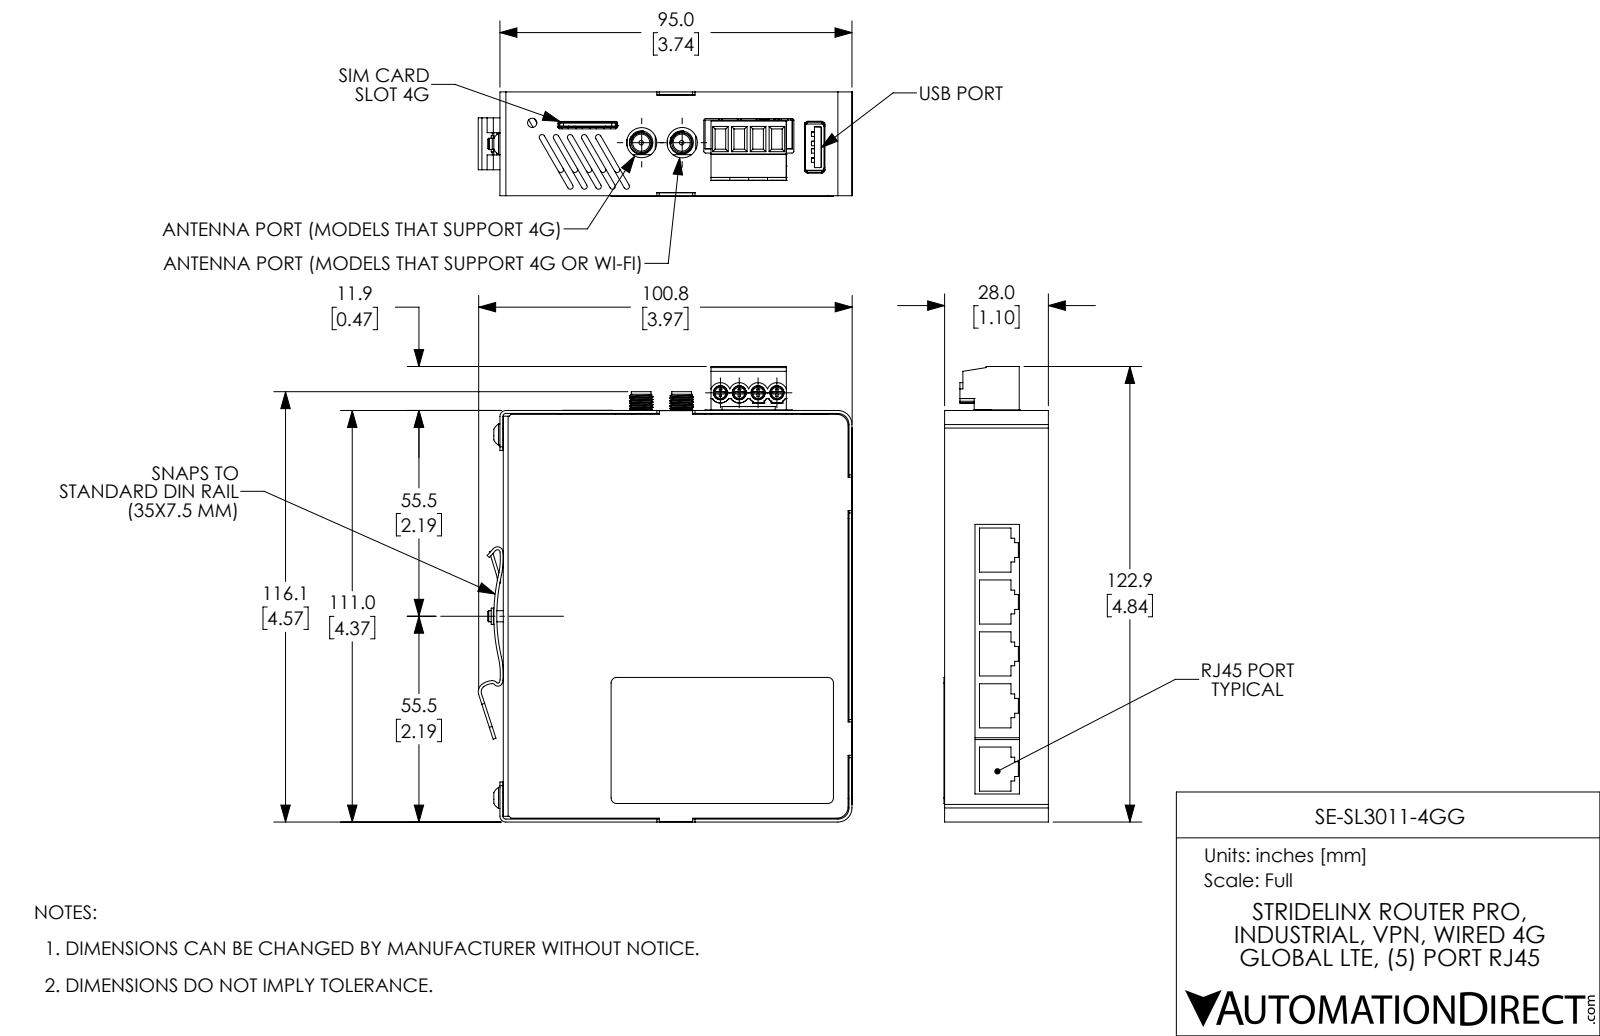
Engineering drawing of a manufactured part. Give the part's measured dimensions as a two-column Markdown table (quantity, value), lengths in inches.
| quantity | value |
| --- | --- |
| part name | SE-SL3011-4GG_R1 |
| STEP written by | SolidWorks 2019 (AUTOMOTIVE_DESIGN) |
| units | inches |
| bodies | 75 solids, 2781 faces (2050 planar, 628 cylindrical, 103 other) |
| overall size | 4.837 × 3.973 × 1.109 |
| volume | 2.859 in³ |
| surface area | 143.9 in² |
| round holes (diameter × count) | 0.079 × 6, 0.098 × 4, 0.15 × 4, 0.048 × 2, 0.138 × 2, 0.183 × 2, 0.008 × 1, 0.118 × 1, 0.128 × 1, 0.157 × 1, 0.173 × 1, 0.212 × 1 |
| round bosses / shafts (diameter × count) | 0.028 × 39, 0.224 × 4, 0.143 × 4, 0.124 × 4, 0.118 × 3, 0.312 × 2, 0.21 × 2, 0.2 × 2 |
| partial cylindrical surfaces (radius × count) | 0.004 × 91, 0.006 × 38, 0.008 × 33, 0.03 × 25, 0.01 × 24, 0.039 × 19, 0.02 × 14, 0.024 × 8 |
| main face-to-face distances | 0.031, 1.071, 1.102, 1.039, 3.673, 4.339, 3.705, 0.038, 1.109, 1.078 |
| hole center spacings | 0.2, 0.1, 0.316, 0.3, 0.361, 0.4, 0.43, 1.615 |
